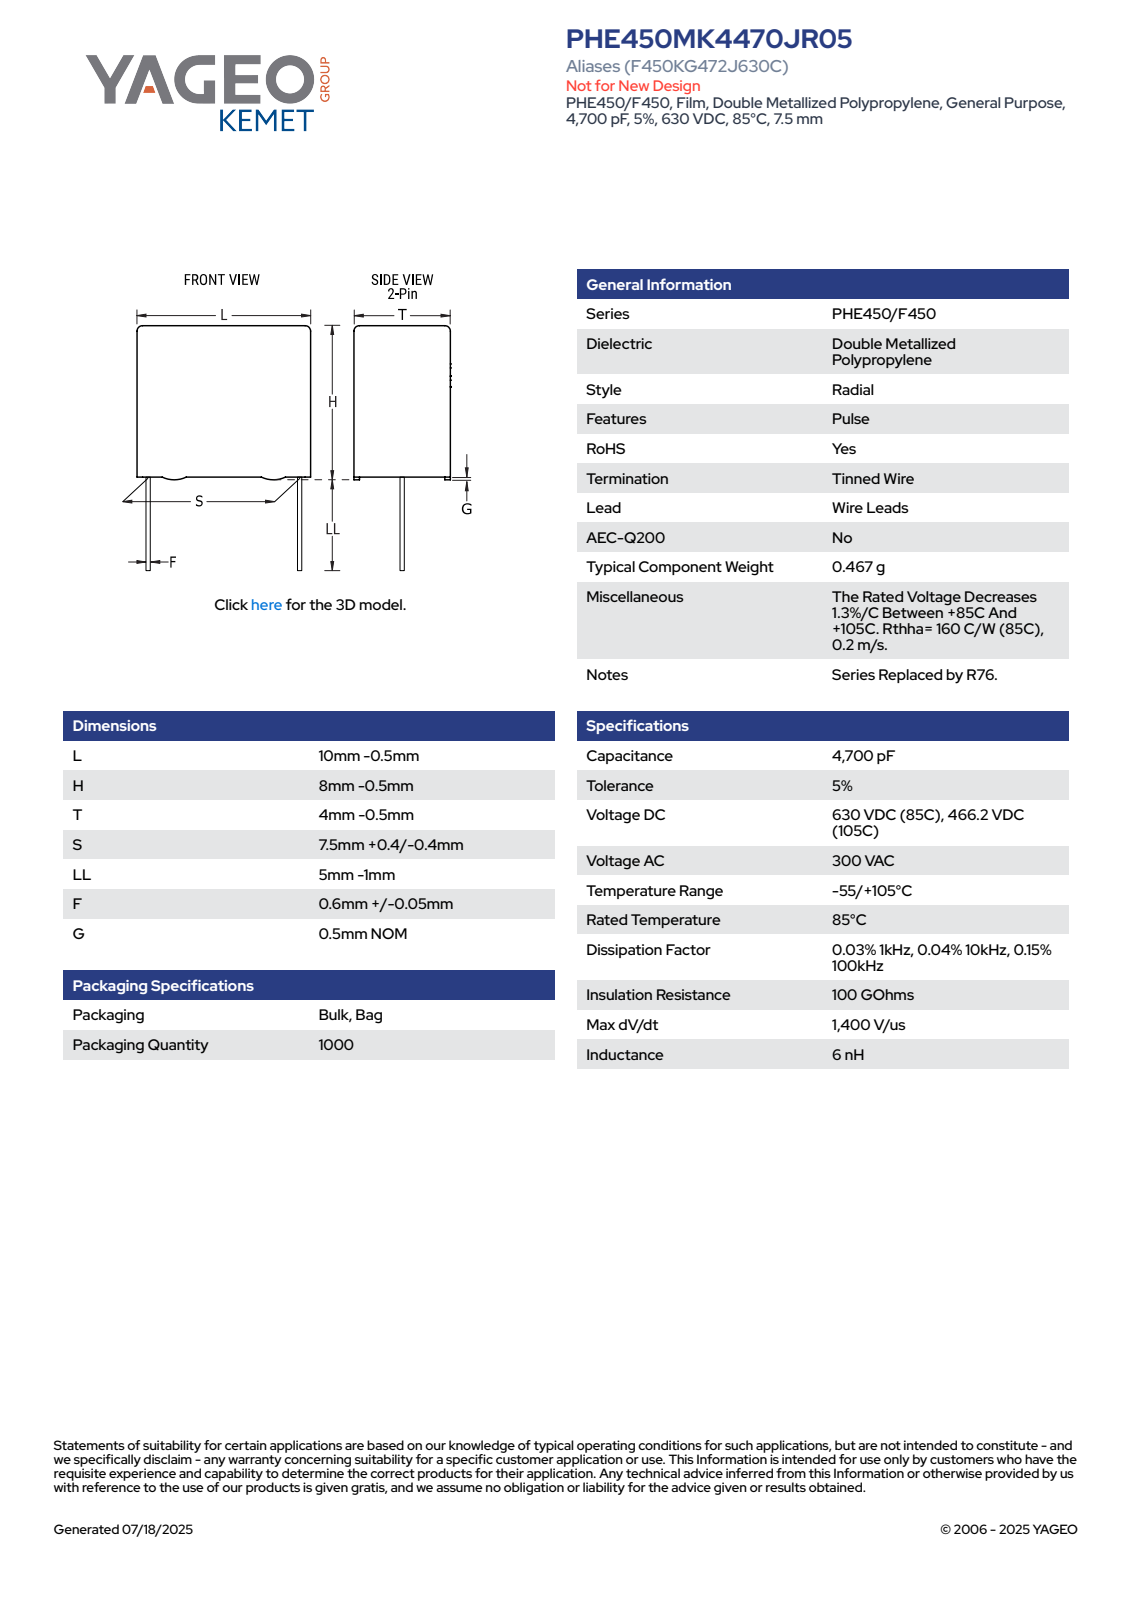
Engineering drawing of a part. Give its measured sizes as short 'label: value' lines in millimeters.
name: CFR_RBG_10X8X4_L9.5H7.5T3.5S7.5LL4F0.65G0.5
written by: SolidWorks 2020 (AUTOMOTIVE_DESIGN)
unit: mm
bodies: 4 solids, 89 faces (81 planar, 8 cylindrical, 0 other)
size: 11.5 × 9.5 × 3.5
volume: 235 mm³; area: 278 mm²
bosses: 2× ⌀0.65
rounds: 4× R0.5
face distances: 3.5, 9.5, 7, 3.3, 3.1, 0.5, 7.5, 4, 4.5, 11.5
